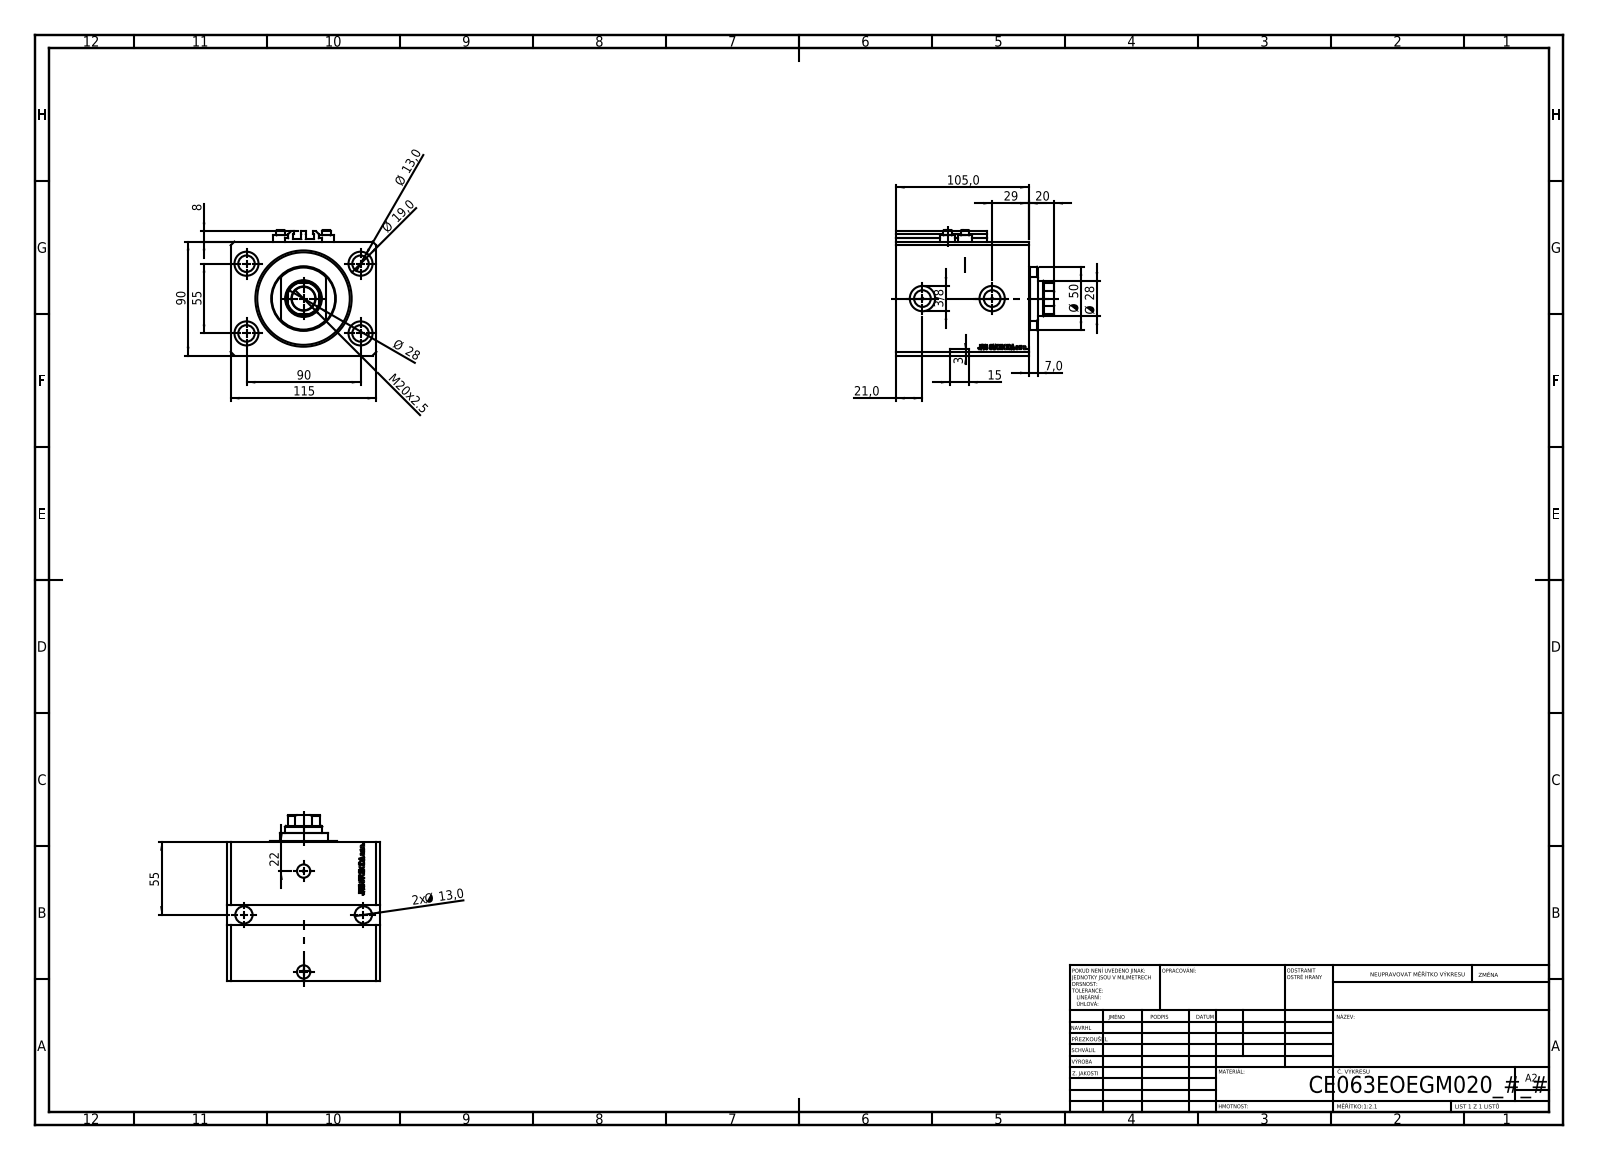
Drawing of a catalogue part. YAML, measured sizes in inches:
part_name: "ALLEN BOLT V250CE; V250CE_VC_E; V250CE_E_Body; V250CE_C_VCP"
step_written_by: "SolidWorks 2019 (CONFIG_CONTROL_DESIGN)"
units: inches
bodies: {solids: 8, faces: 1107, planar: 543, cylindrical: 126, other: 438}
overall_size: [4.921, 4.528, 3.898]
volume: 58.25
surface_area: 238.6
round_holes:
  - {diameter: 0.512, count: 6}
  - {diameter: 0.049, count: 4}
  - {diameter: 0.157, count: 4}
  - {diameter: 0.748, count: 4}
  - {diameter: 0.394, count: 2}
  - {diameter: 0.518, count: 2}
  - {diameter: 0.787, count: 2}
  - {diameter: 0.728, count: 1}
  - {diameter: 1.102, count: 1}
  - {diameter: 2.48, count: 1}
  - {diameter: 2.992, count: 1}
round_bosses_or_shafts:
  - {diameter: 0.457, count: 4}
  - {diameter: 0.276, count: 4}
  - {diameter: 1.969, count: 1}
partial_cylinders:
  - {radius: 0.008, count: 10}
  - {radius: 0.531, count: 1}
face_to_face_distances: [3.543, 0.787, 4.528, 3.346, 4.134, 3.429, 0.705, 2.642, 1.575, 2.559]
hole_center_spacings: [2.076, 2.165, 3.543, 0.535, 1.078, 1.12, 1.324, 1.417]
